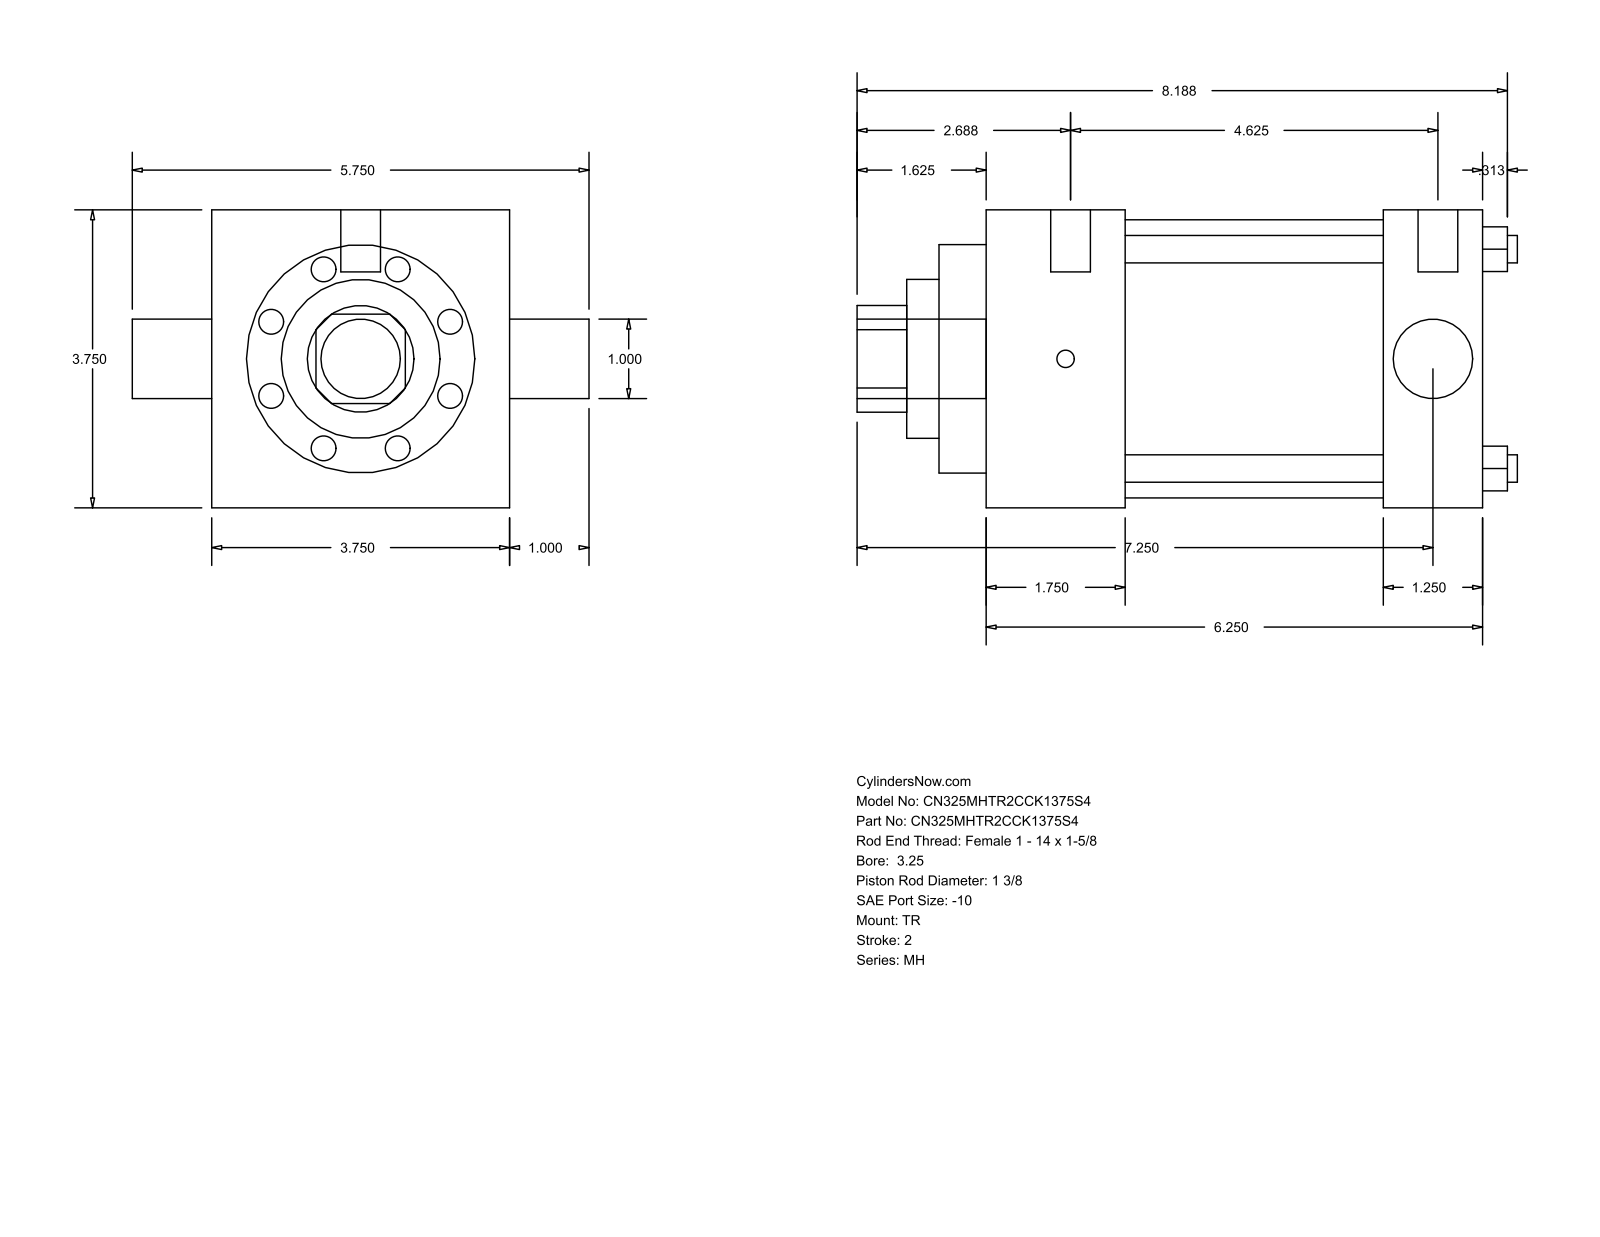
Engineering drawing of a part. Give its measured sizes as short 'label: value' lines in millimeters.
name: MH_TR__0325_1.375
written by: GSSL Pune (CONFIG_CONTROL_DESIGN)
unit: mm
bodies: 0 solids, 86 faces (61 planar, 25 cylindrical, 0 other)
size: 211.14 × 146.05 × 95.25
holes: 4× ⌀8.76, 1× ⌀25.4, 1× ⌀34.92, 1× ⌀50.8, 1× ⌀73.03, 1× ⌀88.9
bosses: 3× ⌀5.56, 2× ⌀12.7, 1× ⌀25.4
rounds: 1× R17.06
face distances: 95.24, 158.76, 44.45, 127.01, 82.56, 114.31, 31.75, 15.08, 59.53, 142.09
hole spacings: 49.57, 70.1, 99.14
